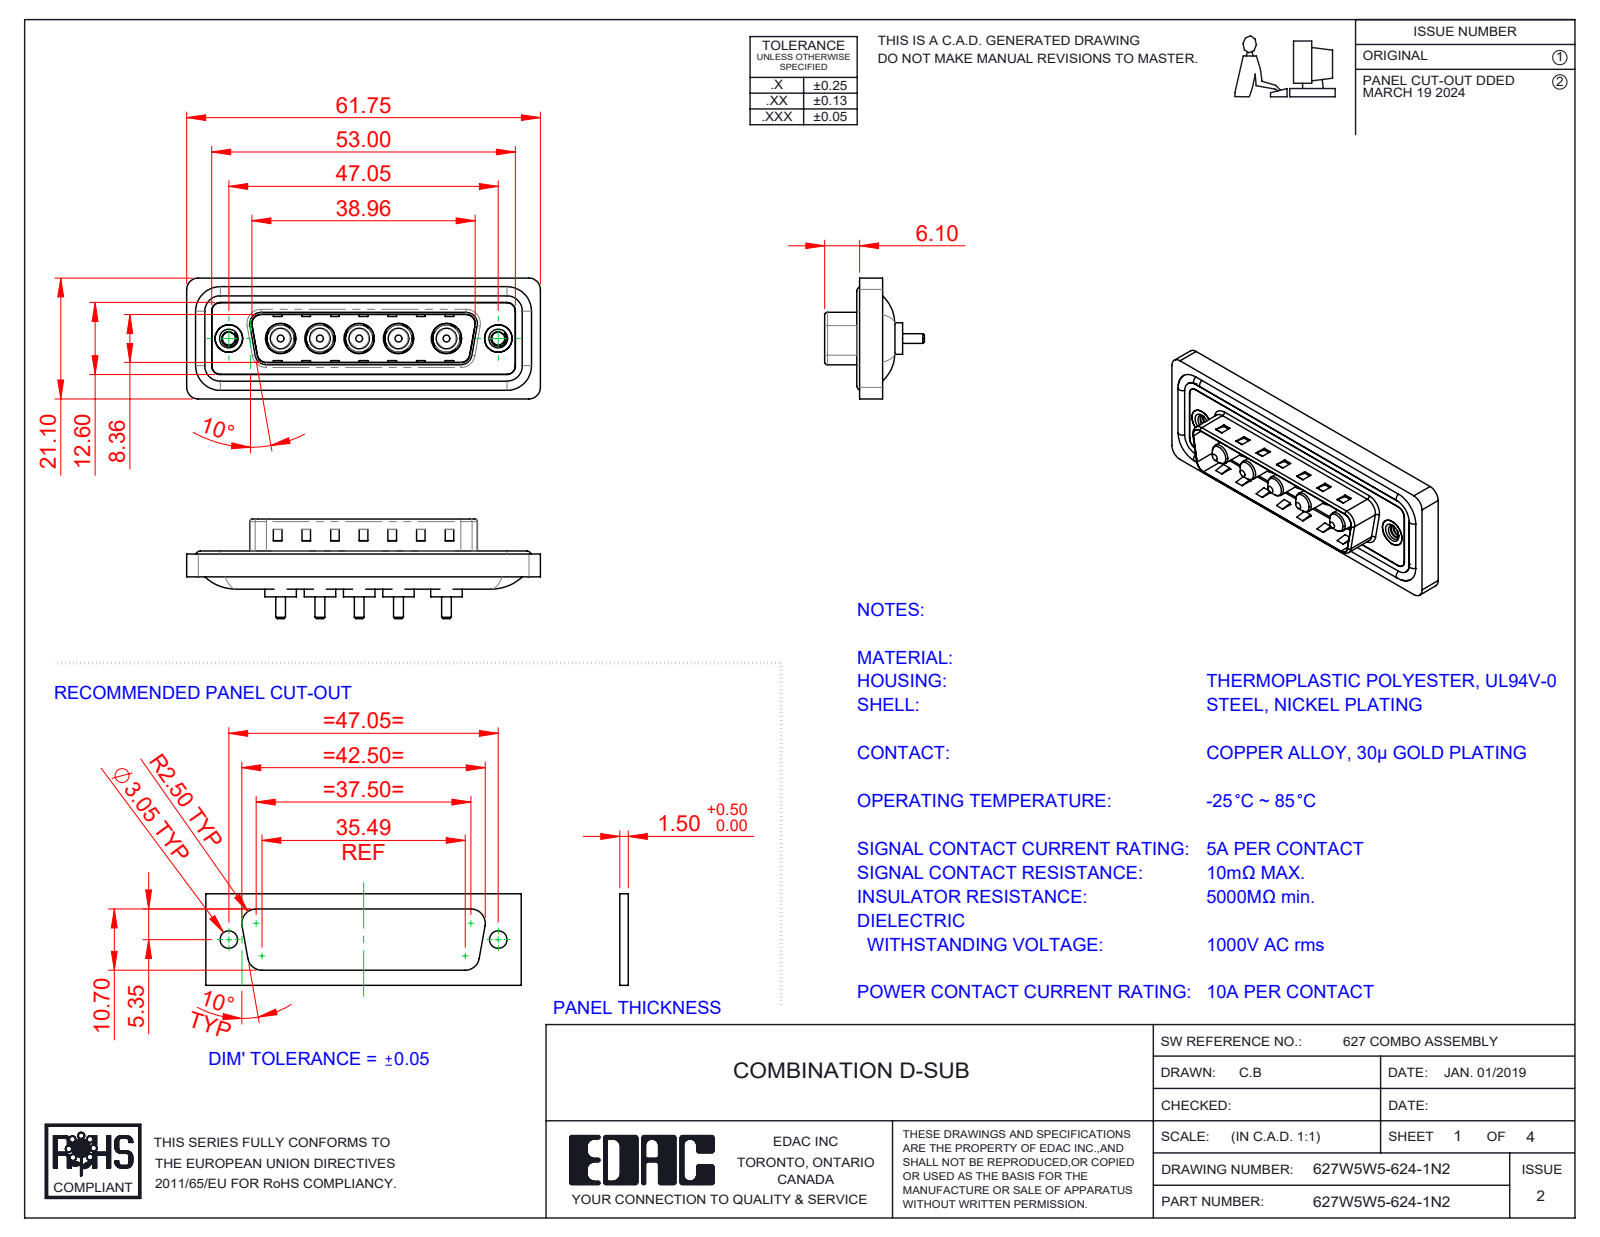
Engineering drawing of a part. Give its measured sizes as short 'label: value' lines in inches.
name: 627Combo Housing_5W5; Power Pin_10A S; 627Combo Waterproof Housing_25 Contacts; 627Combo Shell Front_25 Contacts (+3 more)
written by: SolidWorks 2023 (CONFIG_CONTROL_DESIGN)
unit: in
bodies: 17 solids, 678 faces (259 planar, 283 cylindrical, 136 other)
size: 2.431 × 0.831 × 0.685
volume: 0.452 in³; area: 18.19 in²
holes: 5× ⌀0.191, 5× ⌀0.209, 2× ⌀0.089, 2× ⌀0.157, 2× ⌀0.189, 2× ⌀0.197
bosses: 5× ⌀0.217, 5× ⌀0.205, 5× ⌀0.187, 5× ⌀0.148, 5× ⌀0.142, 5× ⌀0.067, 4× ⌀0.063, 2× ⌀0.193
rounds: 22× R0.059, 18× R0.079, 8× R0.02, 8× R0.063, 5× R0.083, 4× R0.01, 4× R0.024, 4× R0.026
face distances: 0.016, 0.059, 0.02, 0.043, 0.122, 0.063, 0.114, 0.032, 0.377, 0.222
hole spacings: 0.27, 0.356, 0.541, 1.496, 0.27, 0.33, 0.33, 0.356
